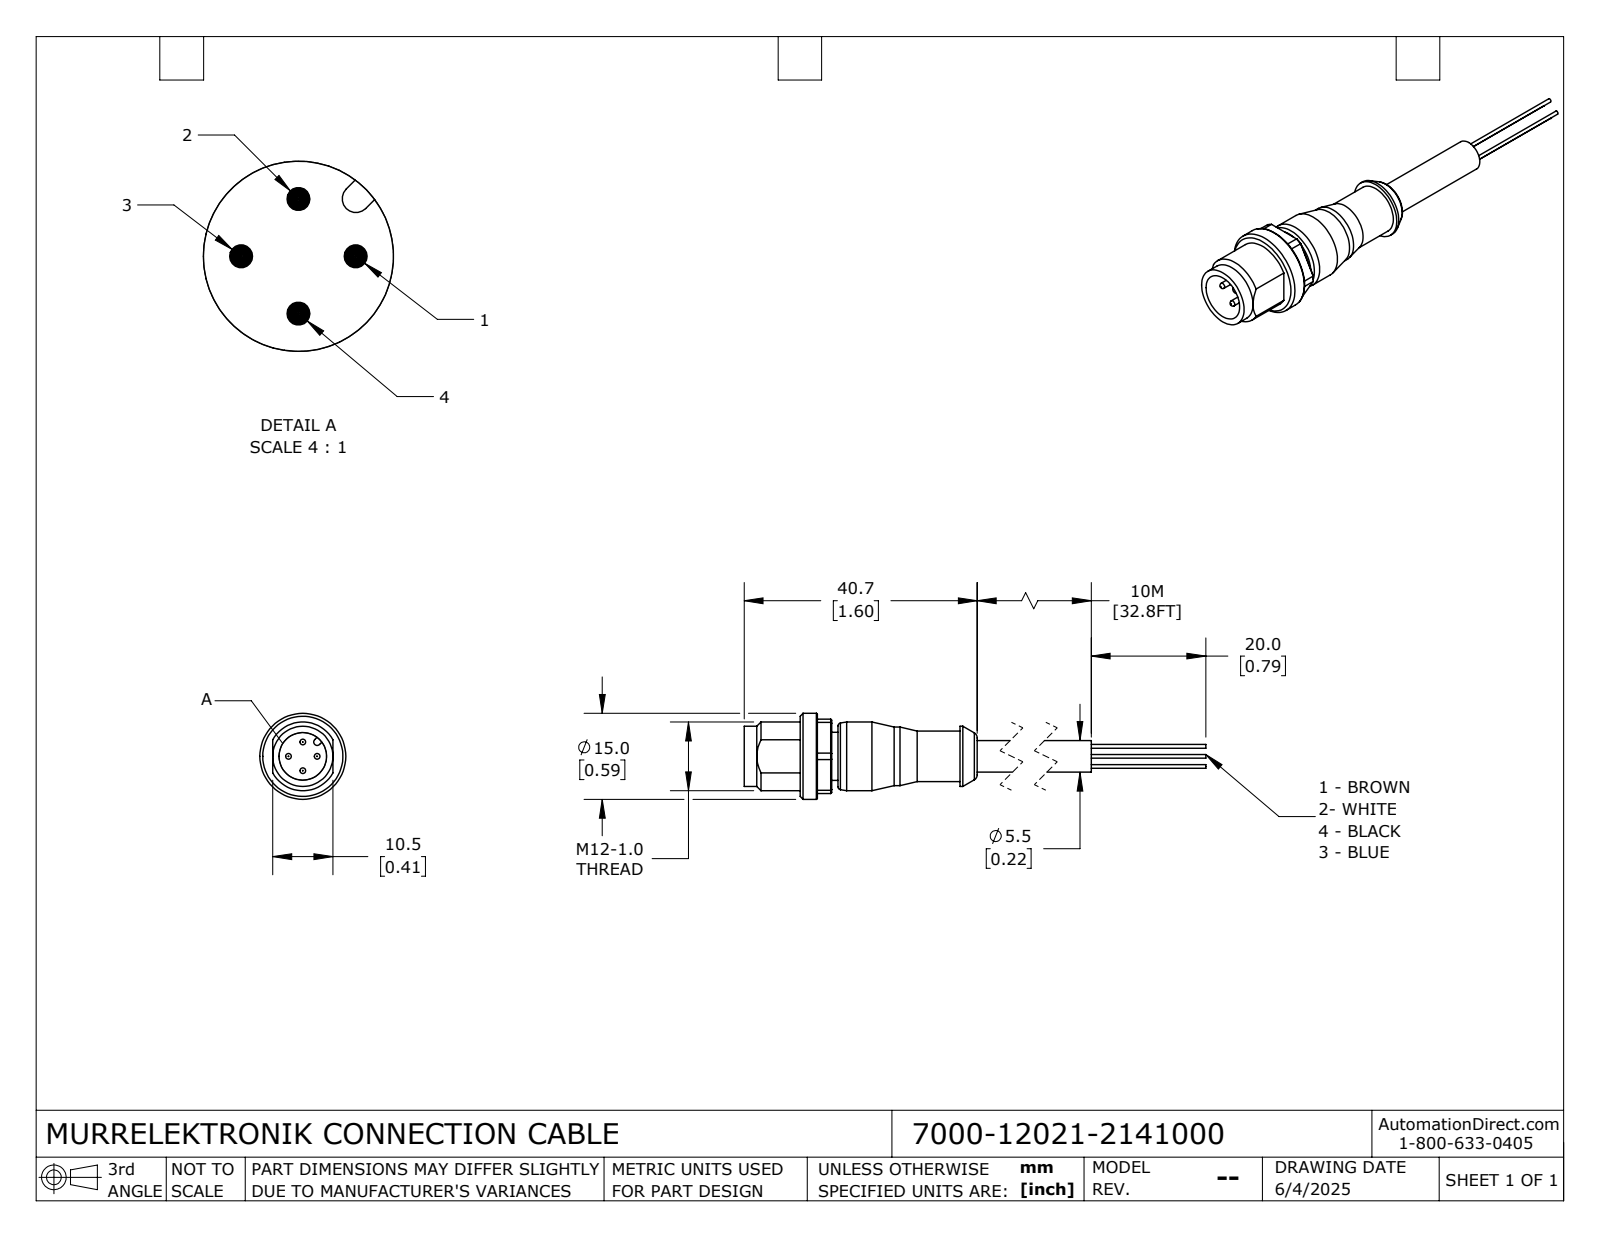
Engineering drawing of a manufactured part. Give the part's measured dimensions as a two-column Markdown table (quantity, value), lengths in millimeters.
| quantity | value |
| --- | --- |
| part name | 7000-12021-2141000 |
| STEP written by | SolidWorks 2024 (CONFIG_CONTROL_DESIGN) |
| units | millimeters |
| bodies | 1 solid, 110 faces (34 planar, 43 cylindrical, 33 other) |
| overall size | 80.7 × 15 × 15 |
| volume | 3 989 mm³ |
| surface area | 2 637 mm² |
| round holes (diameter × count) | 8.3 × 1 |
| round bosses / shafts (diameter × count) | 1 × 4, 0.64 × 4, 15 × 1, 12 × 1, 10.5 × 1, 10.2 × 1, 8.8 × 1, 8.4 × 1 |
| partial cylindrical surfaces (radius × count) | 0.6 × 1, 7.2 × 1 |
| main face-to-face distances | 6.4, 0.9, 5.5, 13, 10.5, 27.9, 7.5, 6.6, 1.1, 8.9 |
